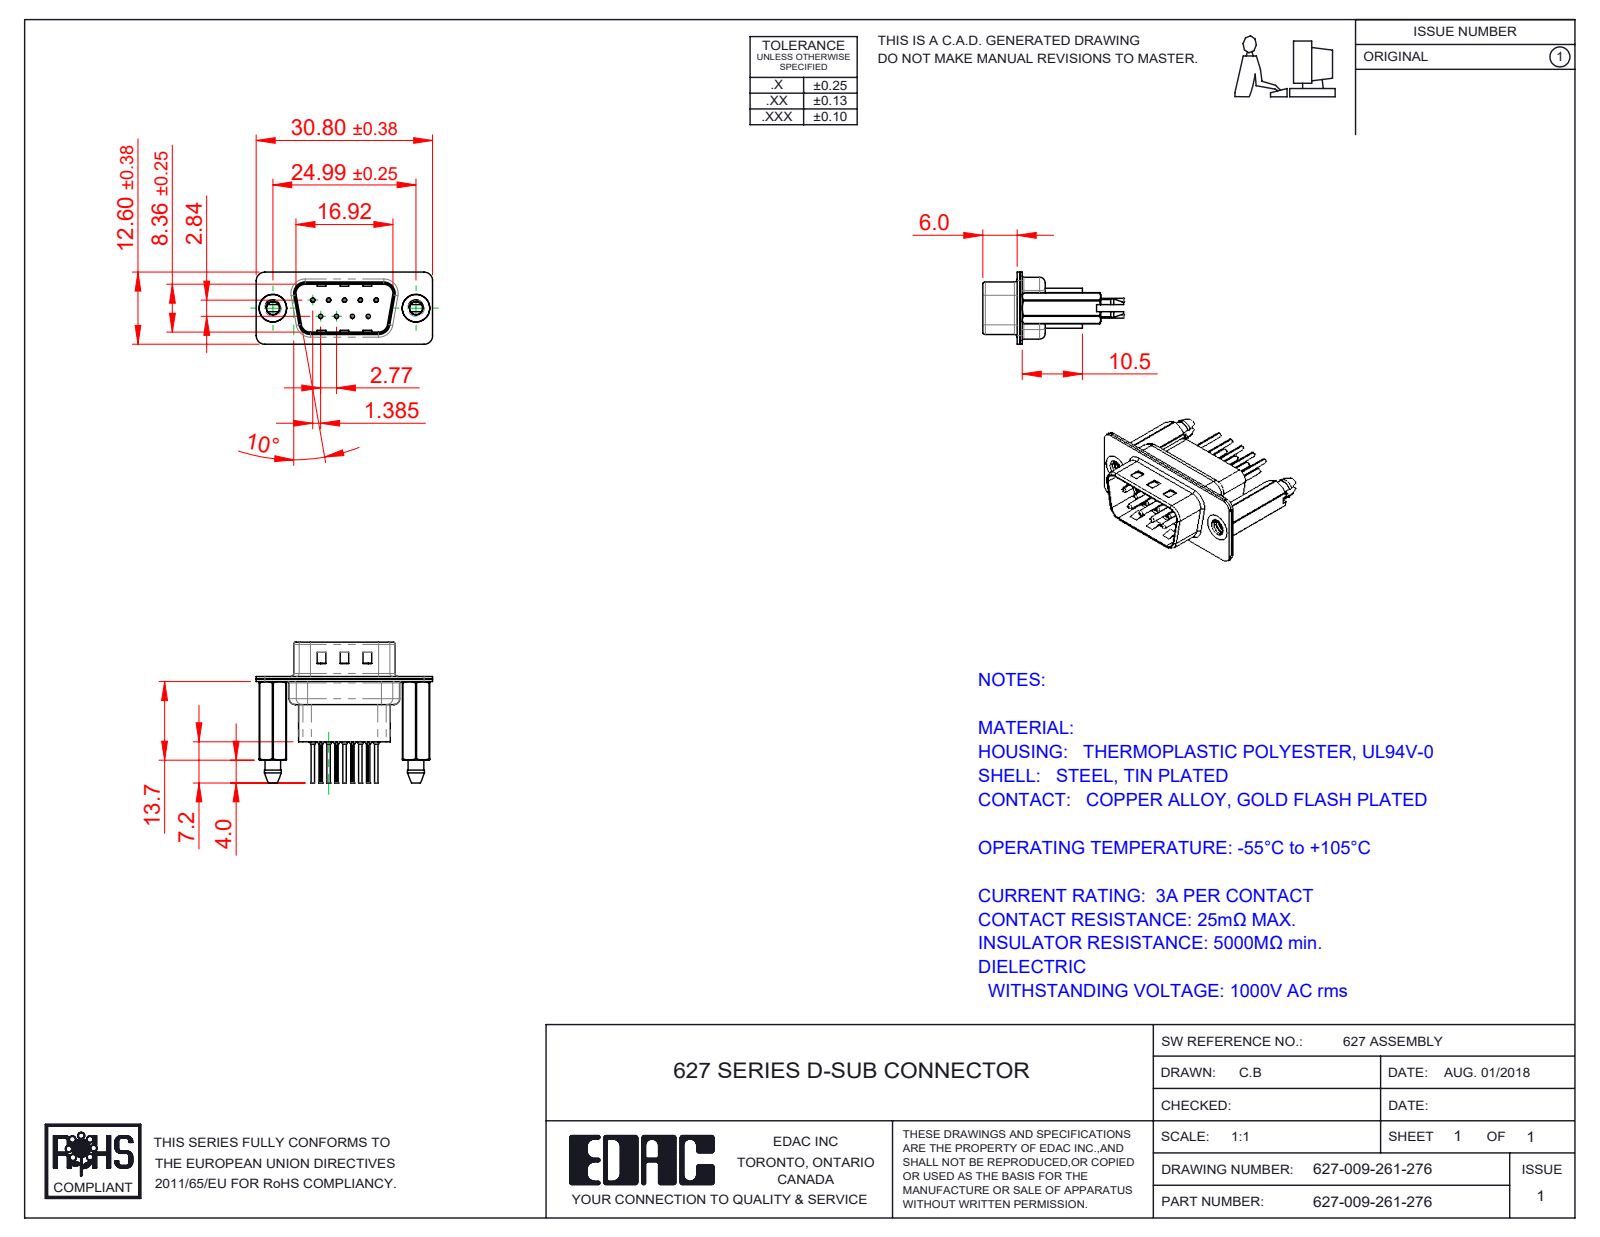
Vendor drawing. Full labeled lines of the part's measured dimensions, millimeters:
Part name (STEP PRODUCT): 627 Contact Row 1_61; 627 Shell Rear_09 Contacts; 627 Housing_09 HP; 627 Shell Front_09 Contacts (+3 more)
STEP written by: SolidWorks 2020 (CONFIG_CONTROL_DESIGN)
Units: millimetres
Bodies: 14 solids, 1294 faces (355 planar, 528 cylindrical, 411 other)
Overall size (bounding box): 30.8 × 24.6 × 12.6
Volume: 2 123 mm³ · Surface area: 5 516 mm²
Round holes (diameter × count): ⌀0.2 ×9, ⌀0.35 ×9, ⌀1.1 ×9, ⌀1.6 ×9, ⌀2.26 ×2, ⌀4 ×2, ⌀4.8 ×2
Round bosses / shafts (diameter × count): ⌀2 ×9, ⌀1.5 ×9, ⌀0.75 ×9, ⌀0.6 ×9, ⌀4.9 ×2
Partial cylindrical surfaces — rounded edges, fillets, slot ends (radius × count): R1.5 ×20, R0.1 ×18, R2 ×12, R1.6 ×10, R0.5 ×8, R0.25 ×4, R0.6 ×4, R0.65 ×4
Main face-to-face distances: 0.45, 0.4, 0.9, 0.82, 9.58, 1.4, 4.76, 1.5, 0.68, 7.68
Hole centre spacings: 3.16, 2.77, 5.54, 5.03, 5.04, 8.31, 7.48, 7.49
